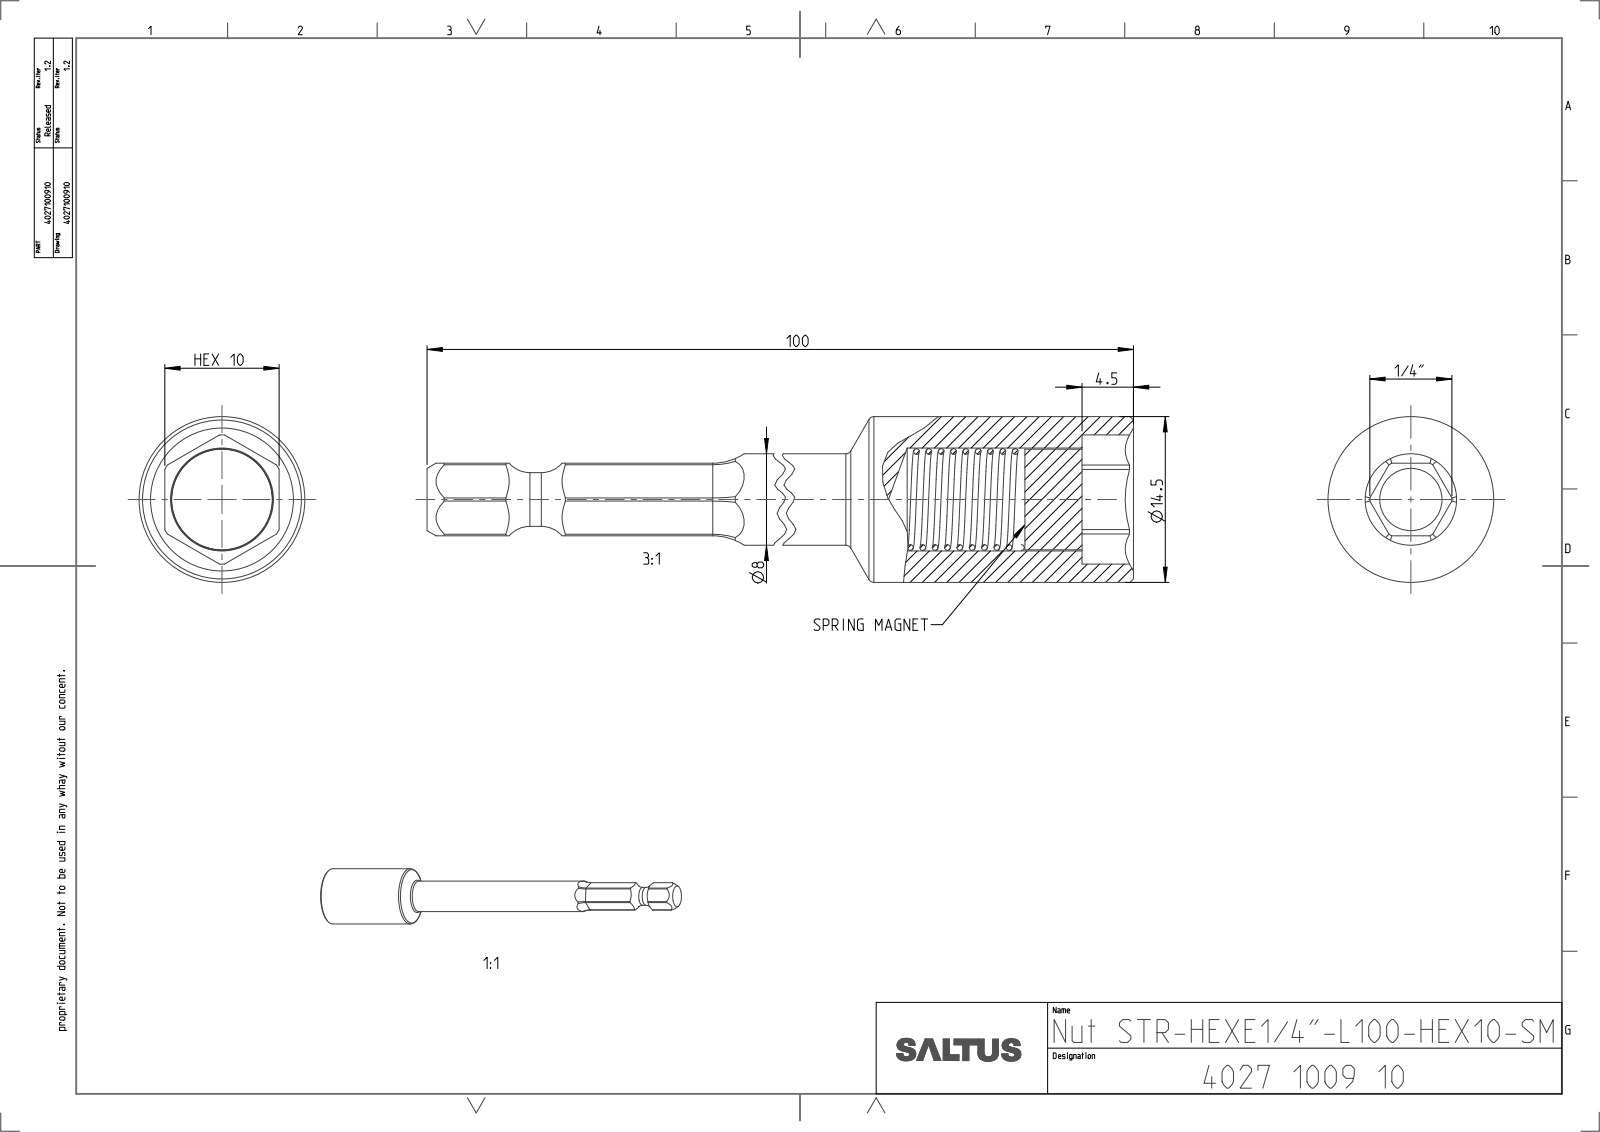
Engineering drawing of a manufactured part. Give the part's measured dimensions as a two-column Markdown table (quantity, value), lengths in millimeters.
| quantity | value |
| --- | --- |
| part name | 4027100910 |
| STEP written by | CREO PARAMETRIC BY PTC INC, 2022414 (CONFIG_CONTROL_DESIGN) |
| units | millimeters |
| bodies | 3 solids, 89 faces (25 planar, 34 cylindrical, 30 other) |
| overall size | 100 × 14.5 × 14.5 |
| volume | 6 222 mm³ |
| surface area | 4 355 mm² |
| round holes (diameter × count) | 9 × 1 |
| round bosses / shafts (diameter × count) | 14.5 × 1, 8.8 × 1, 8 × 1, 4.7 × 1 |
| partial cylindrical surfaces (radius × count) | 5 × 6, 3.59 × 1, 5.65 × 1 |
| main face-to-face distances | 6.34, 6.36, 10, 5, 9.5, 4.5, 90.5, 95.5, 100 |
